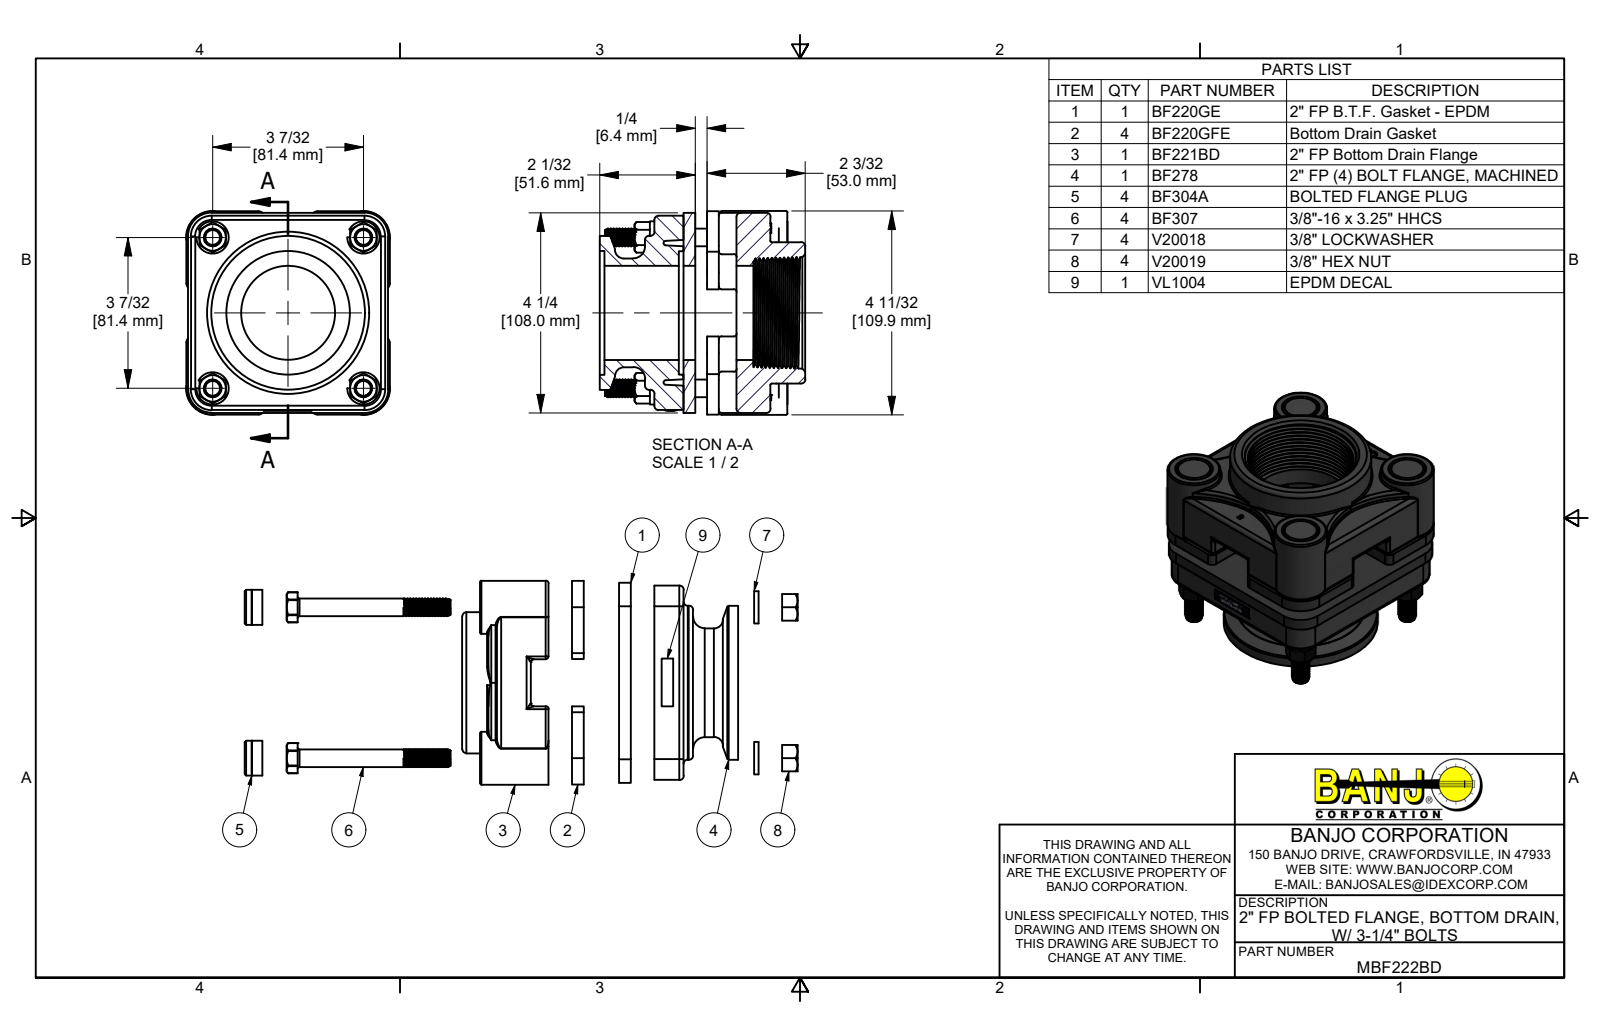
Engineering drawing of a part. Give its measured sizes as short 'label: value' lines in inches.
name: MBF222BD; BF221BD; BF278; V25378X (+7 more)
written by: Autodesk Inventor 2019 (AUTOMOTIVE_DESIGN)
unit: in
bodies: 24 solids, 1275 faces (337 planar, 431 cylindrical, 507 other)
size: 38.212 × 4.328 × 4.328
volume: 35.1 in³; area: 528.2 in²
holes: 4× ⌀0.307, 4× ⌀0.375, 4× ⌀0.38, 4× ⌀0.385, 4× ⌀0.41, 4× ⌀0.438, 4× ⌀0.72, 4× ⌀0.745, 1× ⌀2, 1× ⌀2.62, 1× ⌀2.63, 1× ⌀3
bosses: 60× ⌀0.324, 4× ⌀1.125, 4× ⌀0.742, 4× ⌀0.687, 4× ⌀0.375, 1× ⌀3.27, 1× ⌀2.31
rounds: 44× R0.06, 24× R0.125, 12× R0.09, 8× R0.03, 8× R0.162, 8× R2, 4× R0.32, 4× R0.44
face distances: 0.25, 0.5, 0.25, 0.75, 0.062, 4.187, 0.75, 0.5, 0.25, 0.375
hole spacings: 3.204, 2.265, 2.265, 3.203, 3.204, 4.53, 4.53, 4.531
